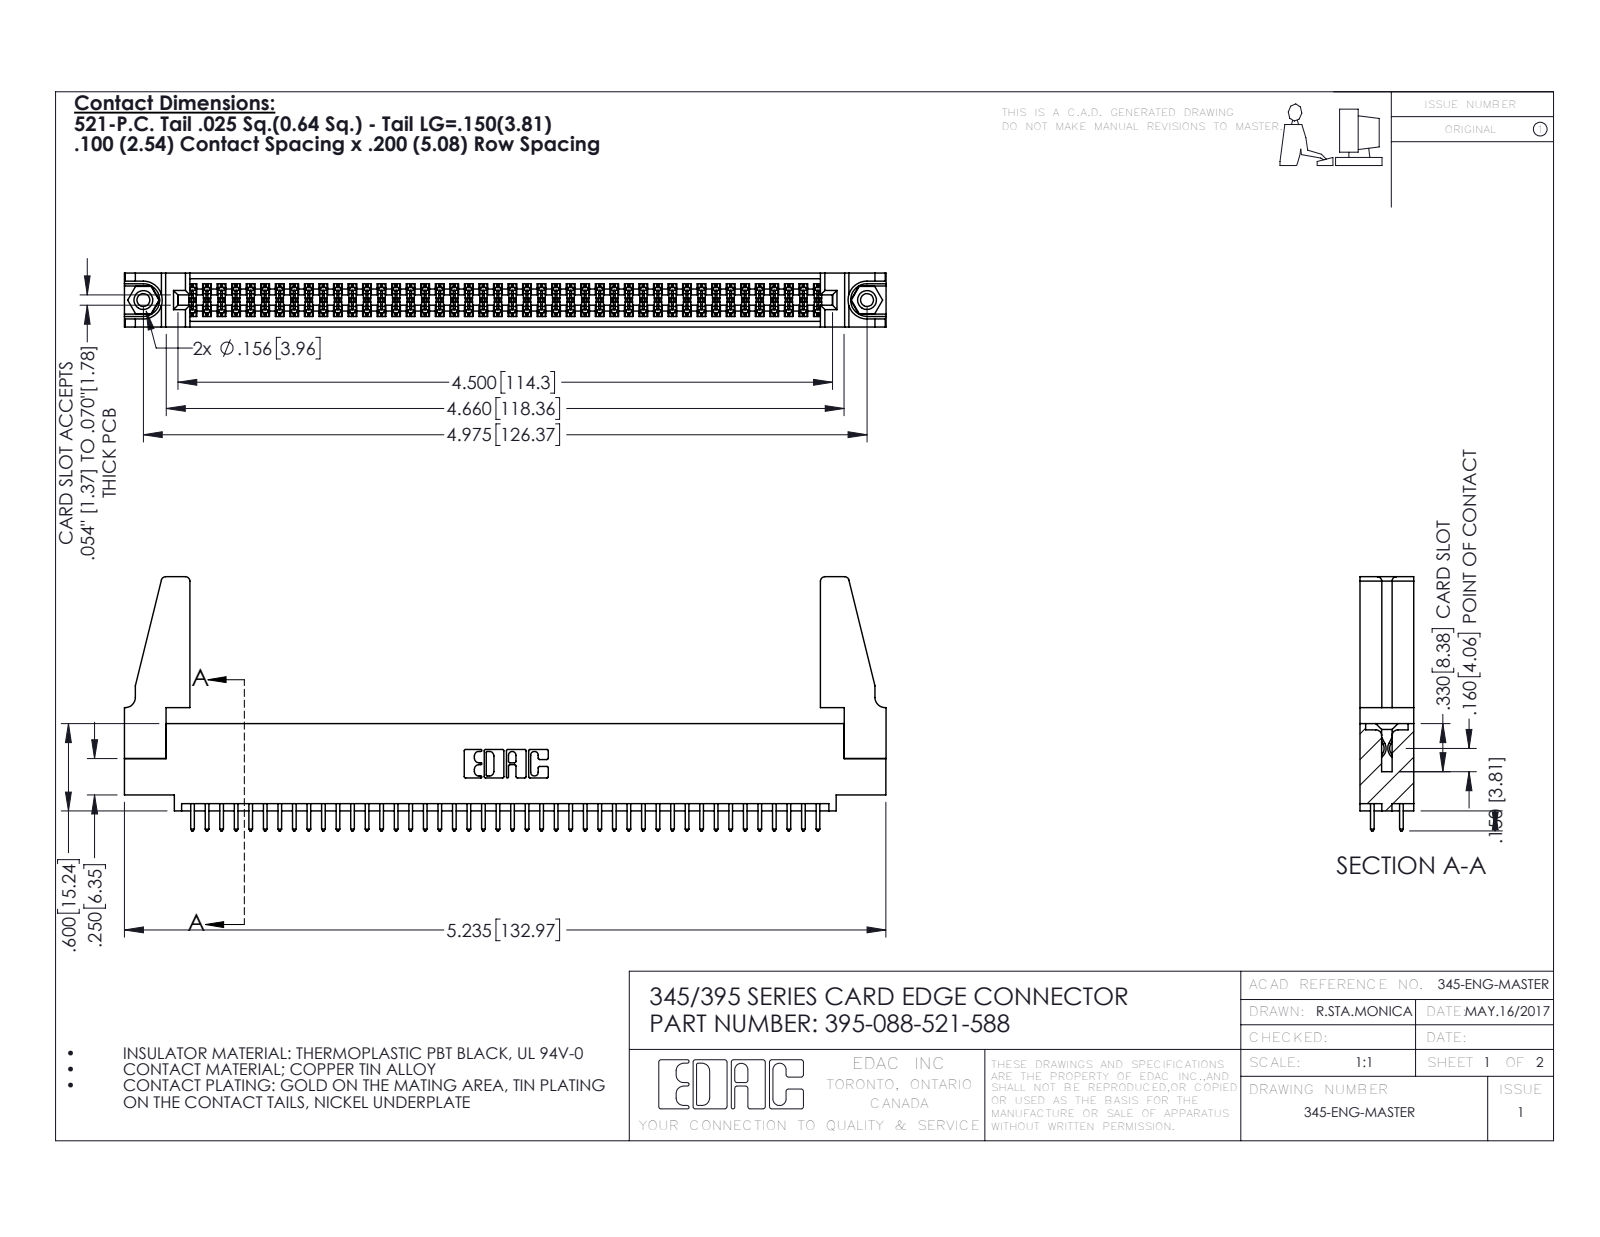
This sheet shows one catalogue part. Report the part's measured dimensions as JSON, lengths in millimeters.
{"part_name": "345-220-078_345-220-088; 345-250-001_345-250-001-102; 345 Part_0.110 Offset - 0.156 Dia-TH; 395-088-521-588 (+1 more)", "step_written_by": "SolidWorks 2016 (CONFIG_CONTROL_DESIGN)", "units": "millimeters", "bodies": {"solids": 93, "faces": 4654, "planar": 3060, "cylindrical": 1578, "other": 16}, "overall_size": [133, 44.4, 9.4], "volume_mm3": 16100, "surface_area_mm2": 21980, "round_holes": [[2.3, 2], [3.2, 2], [4, 2], [1.6, 1]], "round_bosses_or_shafts": [[3.9, 2]], "partial_cylinders_radius": [[0.2, 132], [0.3, 88], [0.3, 22], [0.8, 8], [0.2, 6], [0.8, 6], [0.7, 3], [0.4, 2]], "face_to_face_distances": [1.8, 7.6, 9.4, 5.1, 2.5, 6.9, 0.6, 5.7, 4.4, 3.8], "hole_center_spacings": [6.9, 120.4, 126.4]}
